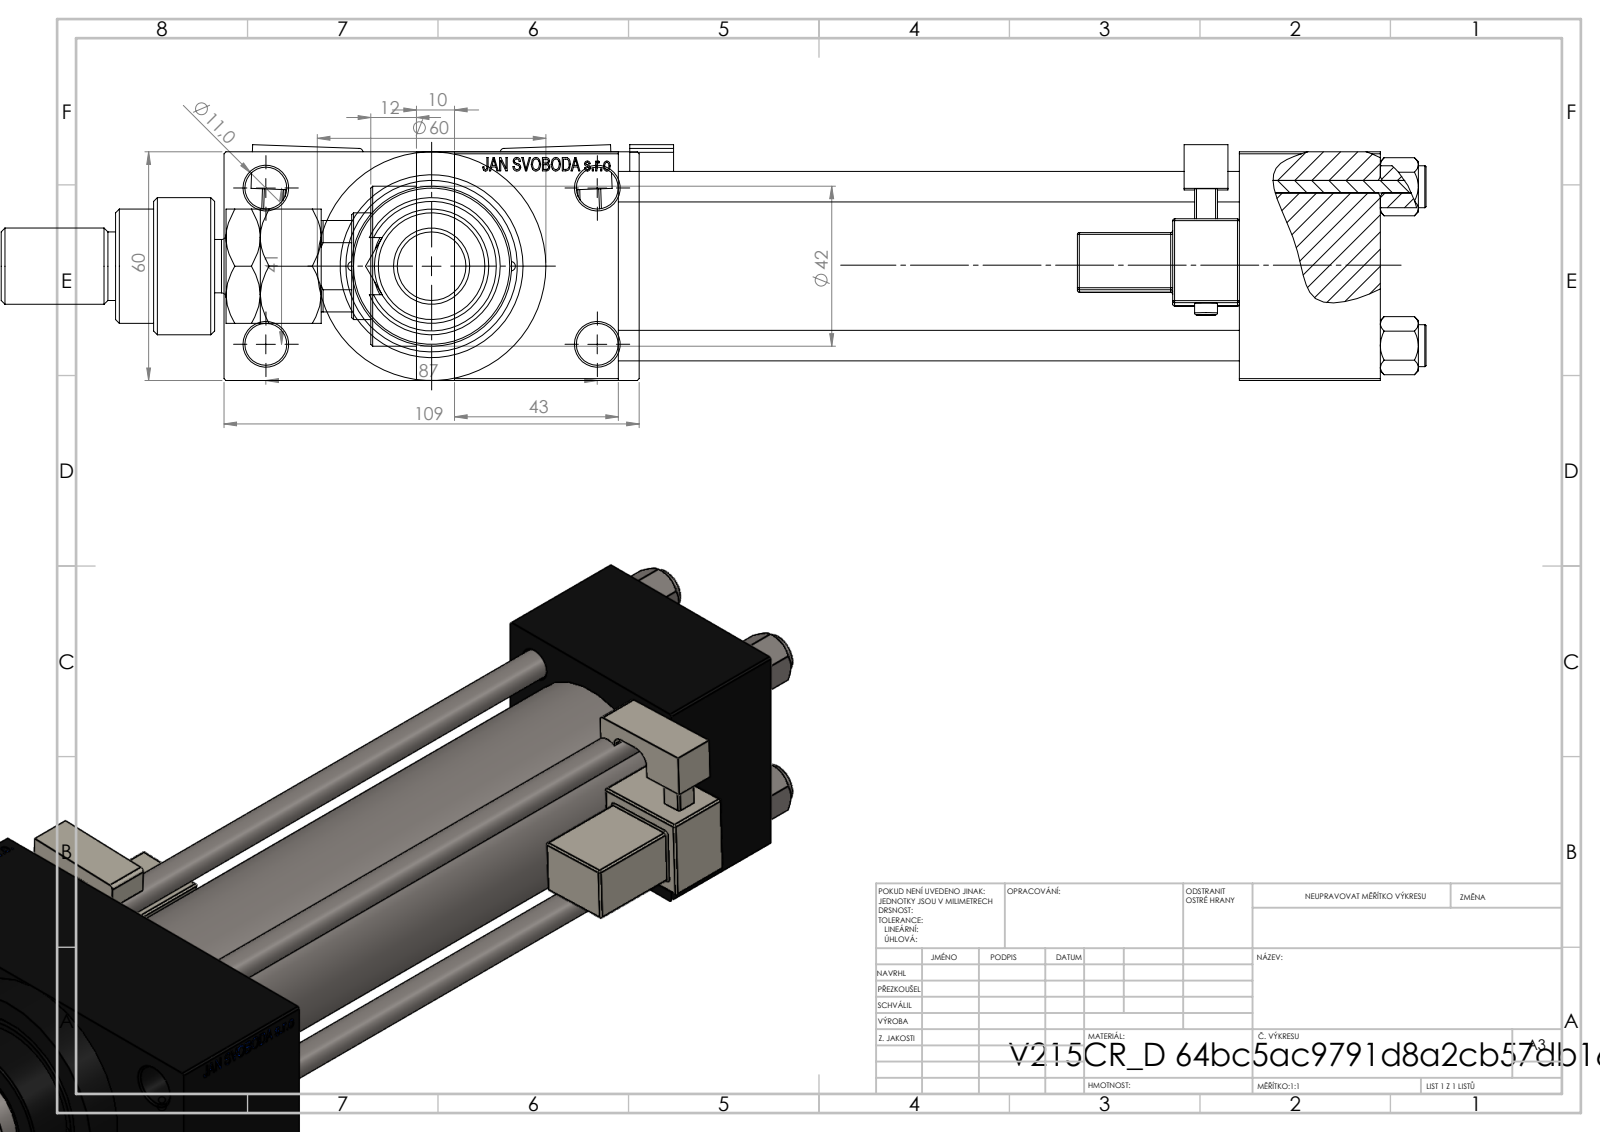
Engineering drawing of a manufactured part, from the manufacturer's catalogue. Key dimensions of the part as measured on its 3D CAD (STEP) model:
Part name (STEP PRODUCT): NUT_M5_D; V215_VC_A; V215CR_VCP_D; MFA (+4 more)
STEP written by: SolidWorks 2019 (CONFIG_CONTROL_DESIGN)
Units: millimetres
Bodies: 15 solids, 1353 faces (588 planar, 165 cylindrical, 600 other)
Overall size (bounding box): 374 × 109 × 61.9
Volume: 746 738 mm³ · Surface area: 202 566 mm²
Round holes (diameter × count): ⌀8 ×4, ⌀11 ×4, ⌀2.5 ×2, ⌀7 ×2, ⌀16.66 ×2, ⌀24 ×2, ⌀18.5 ×1, ⌀28 ×1, ⌀31 ×1, ⌀40 ×1, ⌀45 ×1
Round bosses / shafts (diameter × count): ⌀11 ×4, ⌀6 ×2, ⌀60 ×1, ⌀46 ×1, ⌀42 ×1, ⌀36 ×1, ⌀30 ×1, ⌀22 ×1
Partial cylindrical surfaces — rounded edges, fillets, slot ends (radius × count): R0.5 ×48, R1 ×2, R2.5 ×2, R4 ×2, R7.5 ×1, R12 ×1, R13.5 ×1
Main face-to-face distances: 60, 163, 24.5, 84.5, 37, 200, 43, 243, 206, 109
Hole centre spacings: 20.85, 22.65, 29.49, 30.62, 41.7, 46.53, 47.15, 48.09
